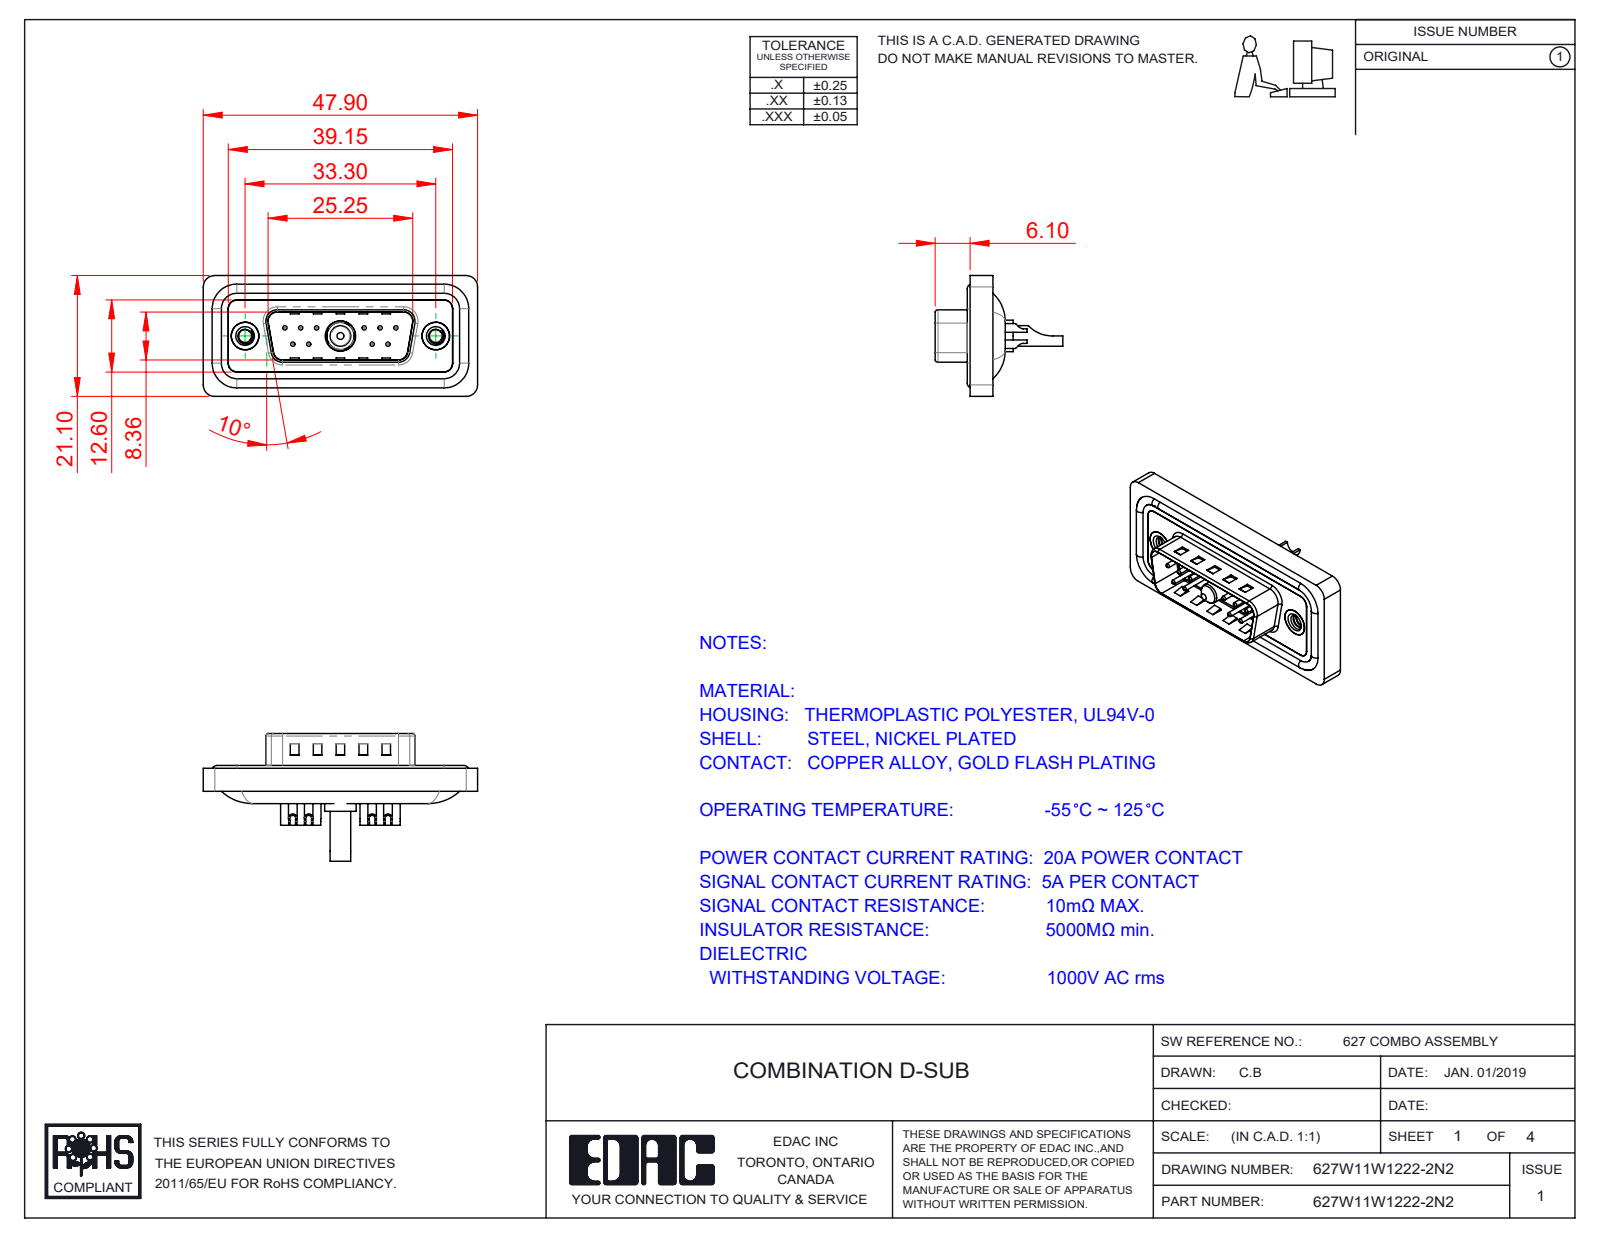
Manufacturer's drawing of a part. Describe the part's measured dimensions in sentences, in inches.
The part is named "627Combo Housing_11W1; 627Combo Shell Front_15 Contacts; 627Combo Contact Row 2_22; 627Combo Threaded Rivet_2 (+5 more)". Its 3-D file was written by "SolidWorks 2020 (CONFIG_CONTROL_DESIGN)". It is 19 solids with 875 faces: 289 planar, 370 cylindrical and 216 other. Overall it measures 1.886 by 0.878 by 0.831 inches. Its volume is 0.334 cubic inches and its surface area 13.95 square inches. Round holes: 10 of diameter 0.03, 10 of diameter 0.039, 10 of diameter 0.063, 10 of diameter 0.079, 2 of diameter 0.089, 2 of diameter 0.157, 2 of diameter 0.189, 2 of diameter 0.197, 1 of diameter 0.106, 1 of diameter 0.191, 1 of diameter 0.209. Round bosses or shafts: 10 of diameter 0.059, 4 of diameter 0.063, 2 of diameter 0.193, 1 of diameter 0.217, 1 of diameter 0.205, 1 of diameter 0.187, 1 of diameter 0.148, 1 of diameter 0.142. Partial cylindrical surfaces (rounded edges, fillets, slot ends): 26 of radius 0.059, 20 of radius 0.079, 9 of radius 0.039, 8 of radius 0.02, 8 of radius 0.063, 4 of radius 0.01, 4 of radius 0.024, 4 of radius 0.026. The main face-to-face distances are 0.016, 0.043, 0.063, 0.059, 0.02, 0.114, 0.122, 0.098, 0.161, 0.032. The hole center spacings are 0.124, 0.109, 0.545, 0.436, 0.654, 0.198, 0.198, 0.218.
